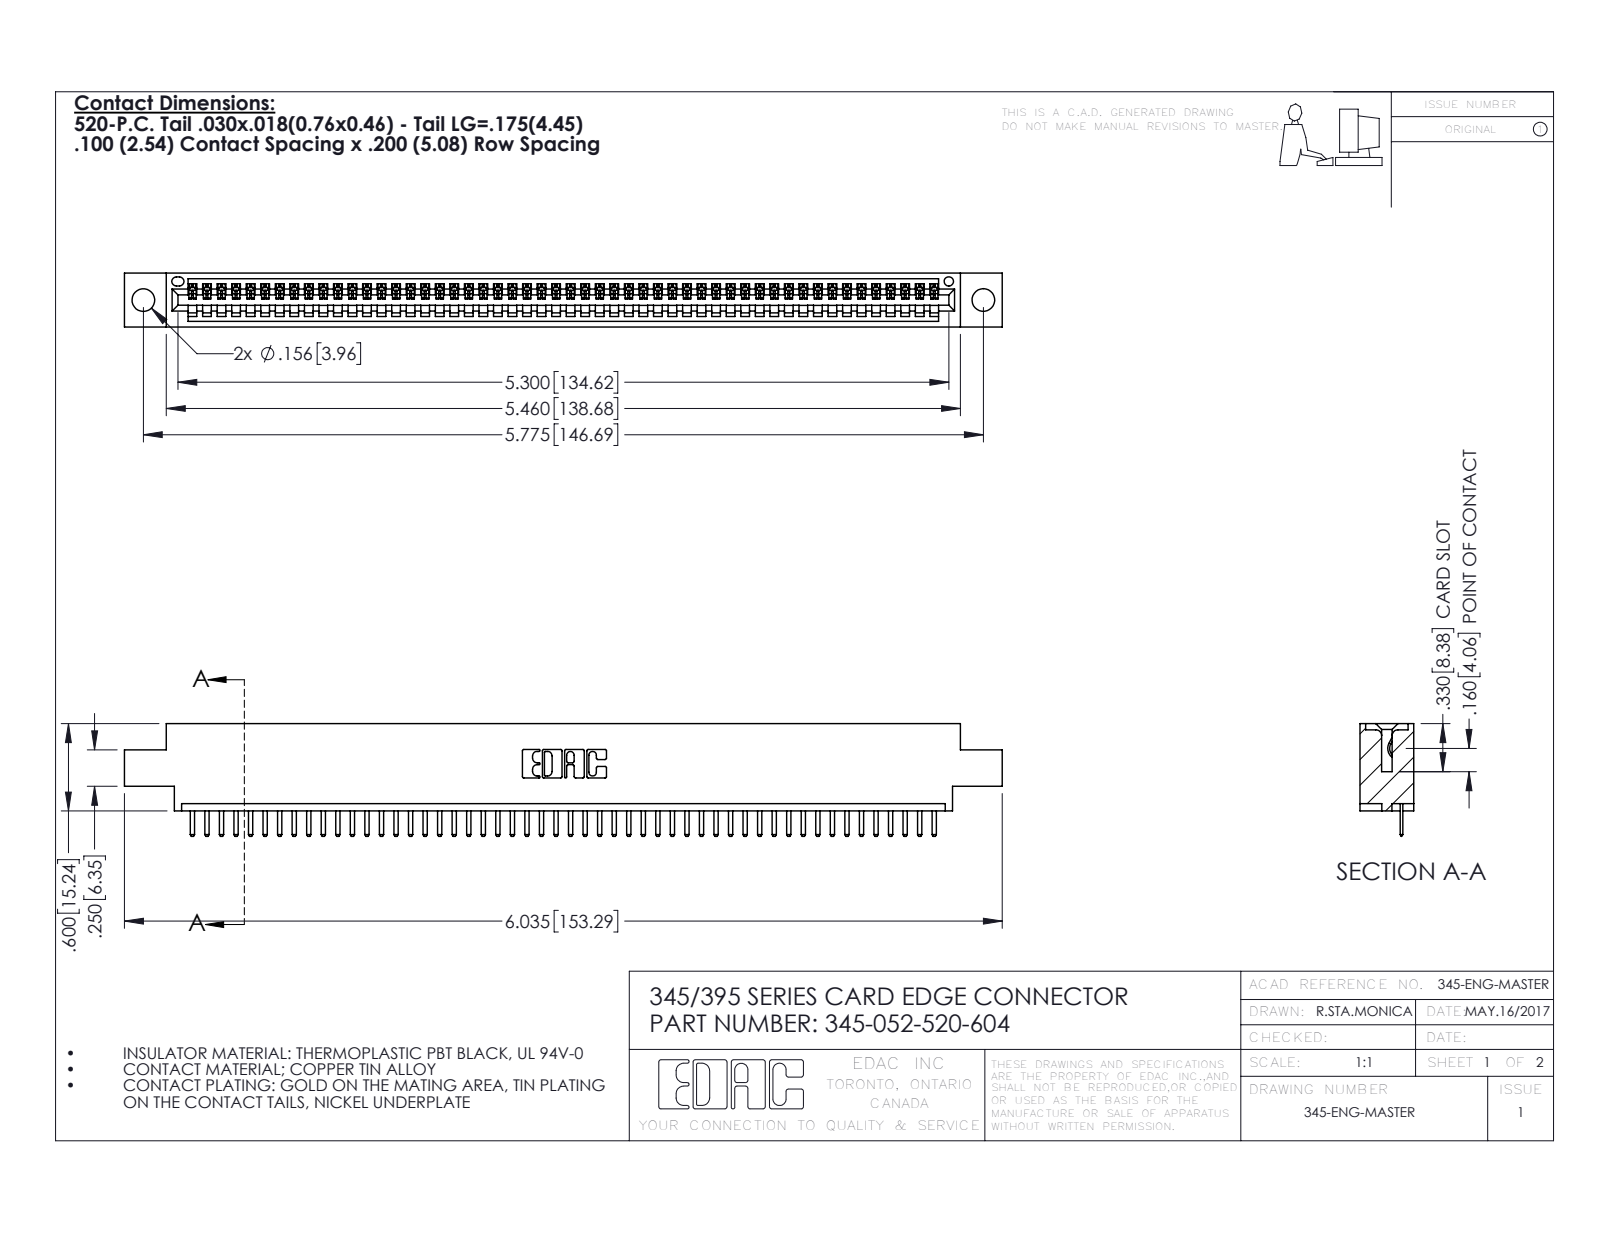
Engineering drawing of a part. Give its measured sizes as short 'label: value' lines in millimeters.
name: 345-292-001_345-293-120; 345-052-520-604; 345 Part_0.170 Offset - 0.156 Dia-TH
written by: SolidWorks 2016 (CONFIG_CONTROL_DESIGN)
unit: mm
bodies: 53 solids, 3354 faces (2268 planar, 1086 cylindrical, 0 other)
size: 153.3 × 19.7 × 9.4
volume: 14 300 mm³; area: 18 570 mm²
holes: 2× ⌀4, 1× ⌀1.6
rounds: 106× R0.3, 104× R0.2, 22× R0.3, 6× R0.2, 6× R0.8, 3× R0.7, 2× R0.8, 2× R1
face distances: 1.8, 7.6, 9.4, 5.1, 2.5, 6.9, 0.6, 5.7, 1.8, 4.4
hole spacings: 6.9, 140.7, 146.7
